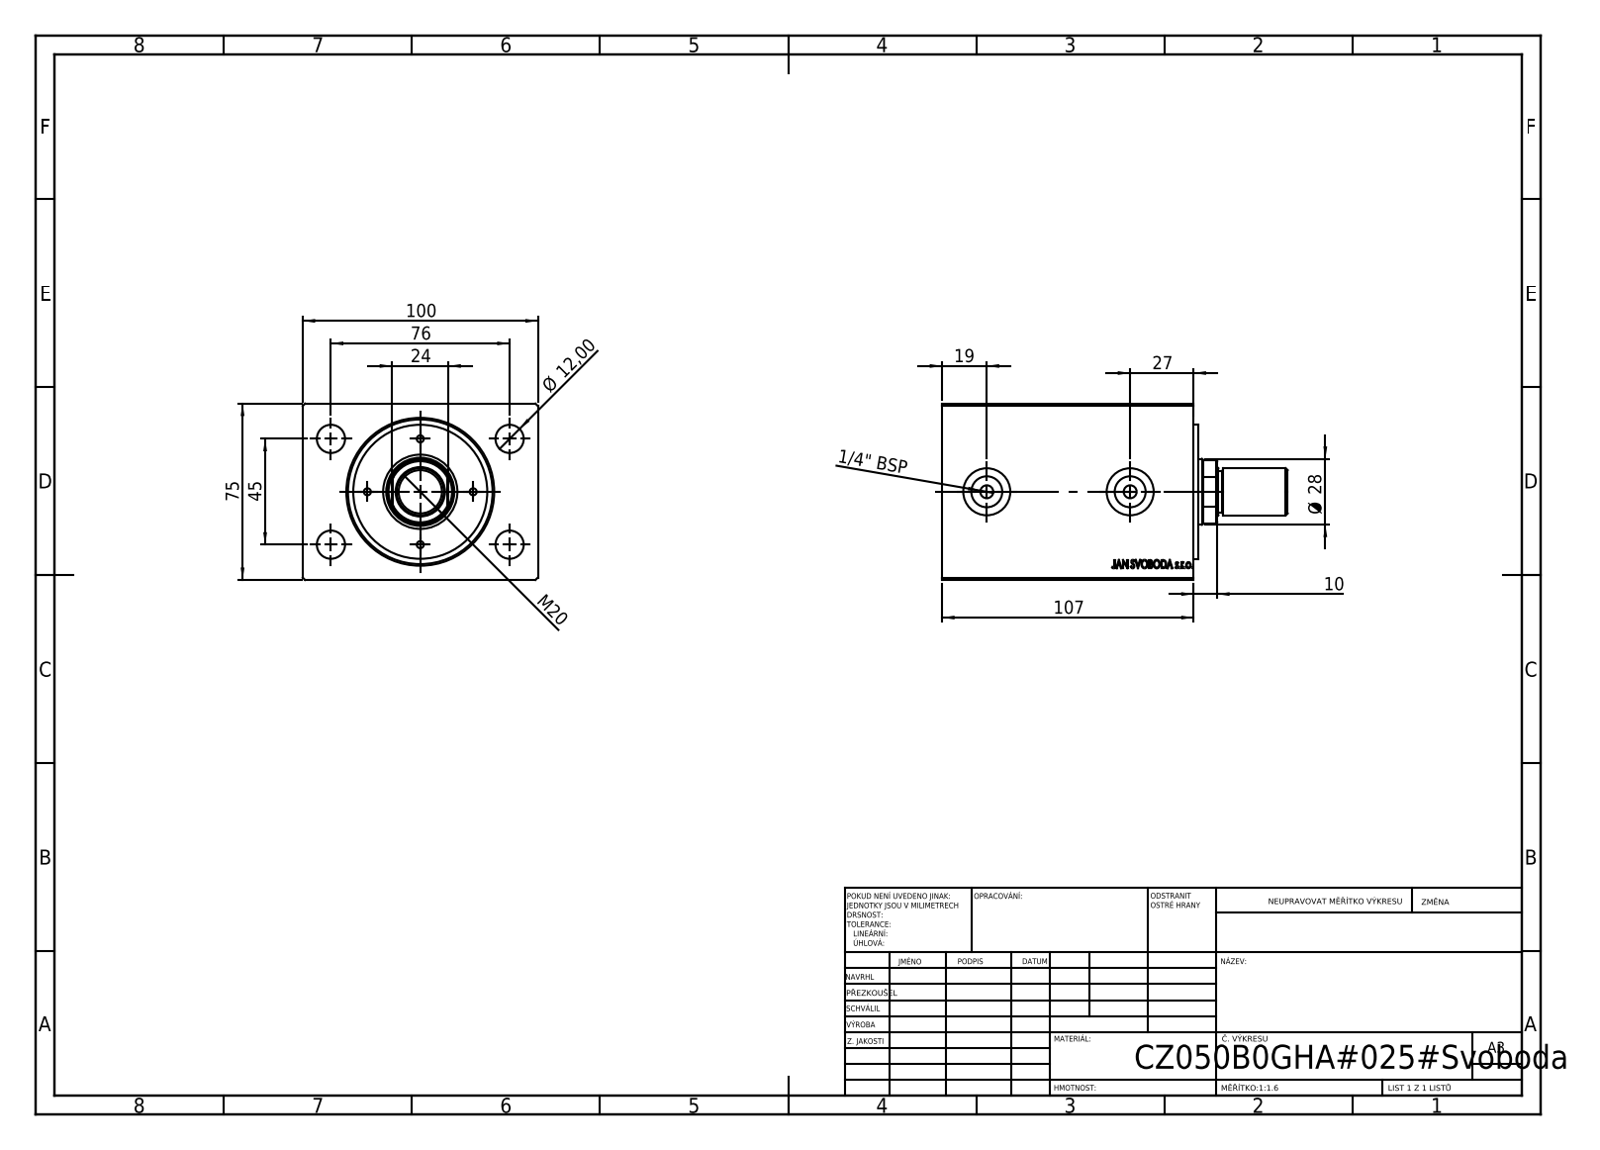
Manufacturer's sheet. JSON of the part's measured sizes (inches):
{"part_name": "V500CZ_MALE_METRIC; V500CZ_B_VC; V500CZ", "step_written_by": "SolidWorks 2019 (CONFIG_CONTROL_DESIGN)", "units": "inches", "bodies": {"solids": 4, "faces": 888, "planar": 404, "cylindrical": 62, "other": 422}, "overall_size": [5.787, 3.937, 2.953], "volume_in3": 45.56, "surface_area_in2": 160.6, "round_holes": [[0.118, 4], [0.472, 4], [0.217, 2], [0.518, 2], [0.787, 2], [0.728, 1], [1.102, 1], [1.142, 1], [1.417, 1], [1.969, 1], [2.421, 1]], "round_bosses_or_shafts": [[2.244, 1], [0.787, 1], [0.709, 1]], "partial_cylinders_radius": [[0.531, 1]], "face_to_face_distances": [2.953, 3.937, 4.213, 3.512, 0.701, 0.394, 0.323, 0.071, 3.189, 3.89], "hole_center_spacings": [0.886, 1.076, 1.253, 1.496, 1.739, 1.772, 2.319, 2.541]}
